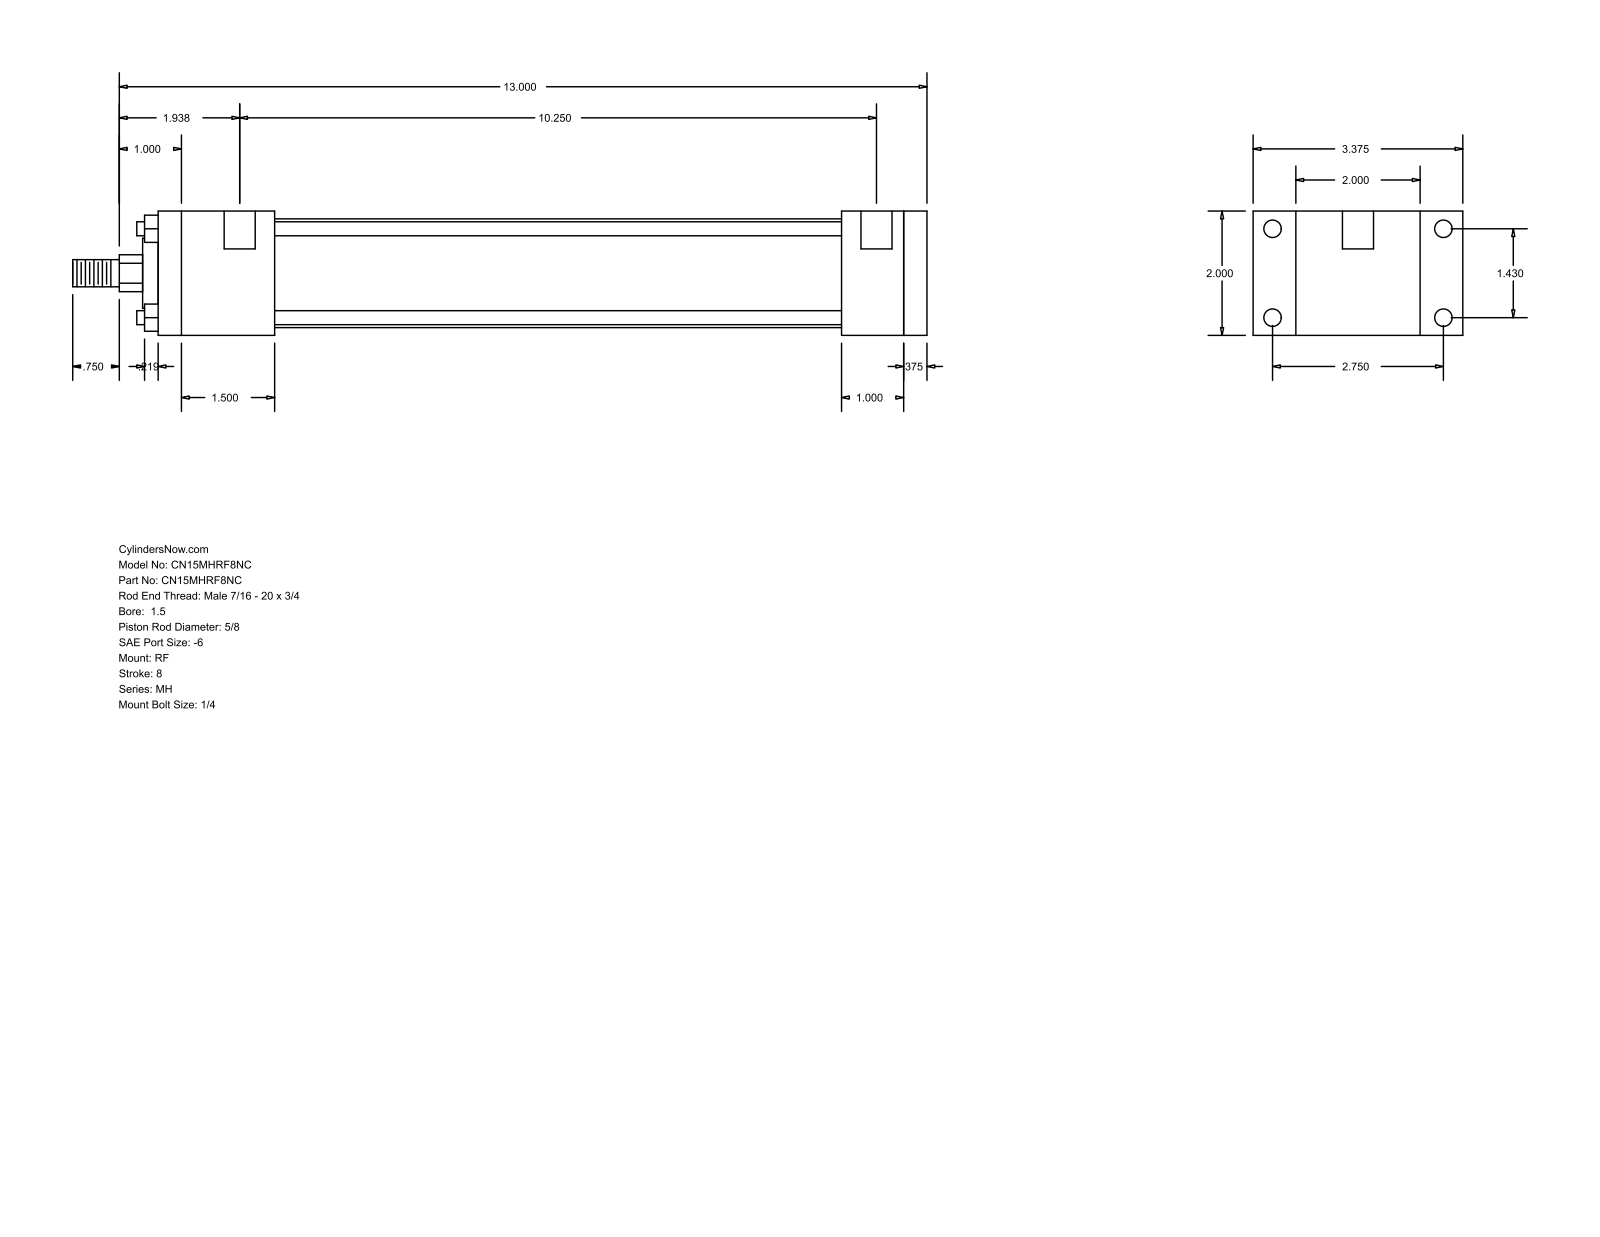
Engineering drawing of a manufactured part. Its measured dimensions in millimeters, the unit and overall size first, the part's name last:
Units: millimetres
Overall size (bounding box): 349.25 × 85.72 × 50.8
Round holes (diameter × count): ⌀5.56 ×4, ⌀7.14 ×4, ⌀12.7 ×2
Round bosses / shafts (diameter × count): ⌀5.71 ×4, ⌀44.45 ×1, ⌀28.57 ×1, ⌀15.88 ×1, ⌀11.11 ×1
Partial cylindrical surfaces — rounded edges, fillets, slot ends (radius × count): R7.54 ×1
Main face-to-face distances: 50.8, 9.52, 314.32, 304.8, 34.93, 17.46, 68.26, 279.39, 25.41, 47.62
Hole centre spacings: 36.32, 69.84, 78.72, 263.52, 3.17, 260.35
Bodies: 0 solids, 92 faces (64 planar, 28 cylindrical, 0 other)
Part name (STEP PRODUCT): MH_RF__0150_0.625
STEP written by: GSSL Pune (CONFIG_CONTROL_DESIGN)
